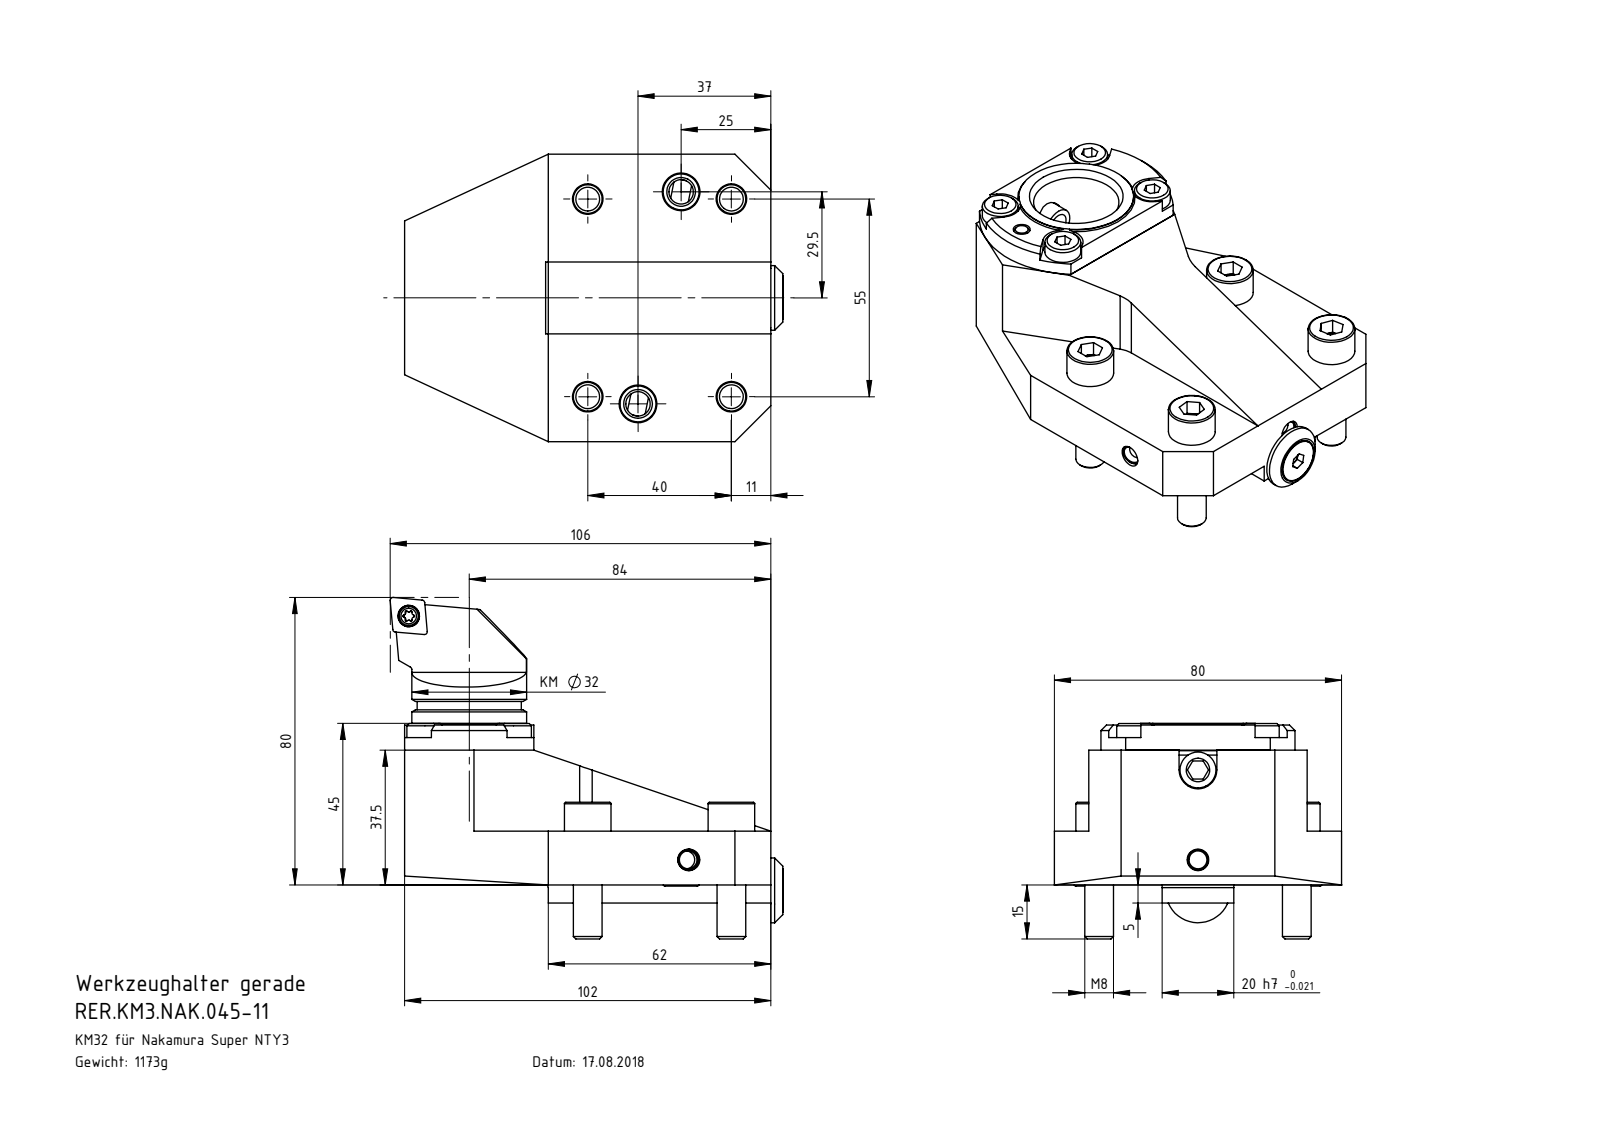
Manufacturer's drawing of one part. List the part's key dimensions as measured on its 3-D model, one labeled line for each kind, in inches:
Part name (STEP PRODUCT): RER-KM3.NAK.045-11_A; RER.KM3.NAK.045-11; DIN 3771 - 25.07x2.62; DIN 3771 - 8x1 (+5 more)
STEP written by: SolidWorks 2017 (AUTOMOTIVE_DESIGN)
Units: inches
Bodies: 25 solids, 598 faces (198 planar, 171 cylindrical, 229 other)
Overall size (bounding box): 4.15 × 3.15 × 2.362
Volume: 10.72 in³ · Surface area: 82.47 in²
Round holes (diameter × count): ⌀0.197 ×10, ⌀0.268 ×6, ⌀0.335 ×4, ⌀0.236 ×2, ⌀0.413 ×2, ⌀0.187 ×1, ⌀0.236 ×1, ⌀0.252 ×1, ⌀0.369 ×1, ⌀0.867 ×1, ⌀0.902 ×1, ⌀1.26 ×1
Round bosses / shafts (diameter × count): ⌀0.236 ×8, ⌀0.394 ×5, ⌀0.512 ×4, ⌀0.315 ×4, ⌀1.259 ×1, ⌀1.258 ×1, ⌀1.248 ×1, ⌀0.709 ×1
Partial cylindrical surfaces — rounded edges, fillets, slot ends (radius × count): R0.221 ×4, R0.276 ×2, R0.031 ×1, R0.124 ×1, R0.124 ×1, R0.207 ×1, R1.063 ×1
Main face-to-face distances: 0.591, 0.886, 1.476, 0.787, 0.197, 1.673, 4.016, 1.181, 2.067, 0.138
Hole centre spacings: 0.846, 0.509, 0.557, 0.902, 0.971, 1.027, 1.387, 1.575
